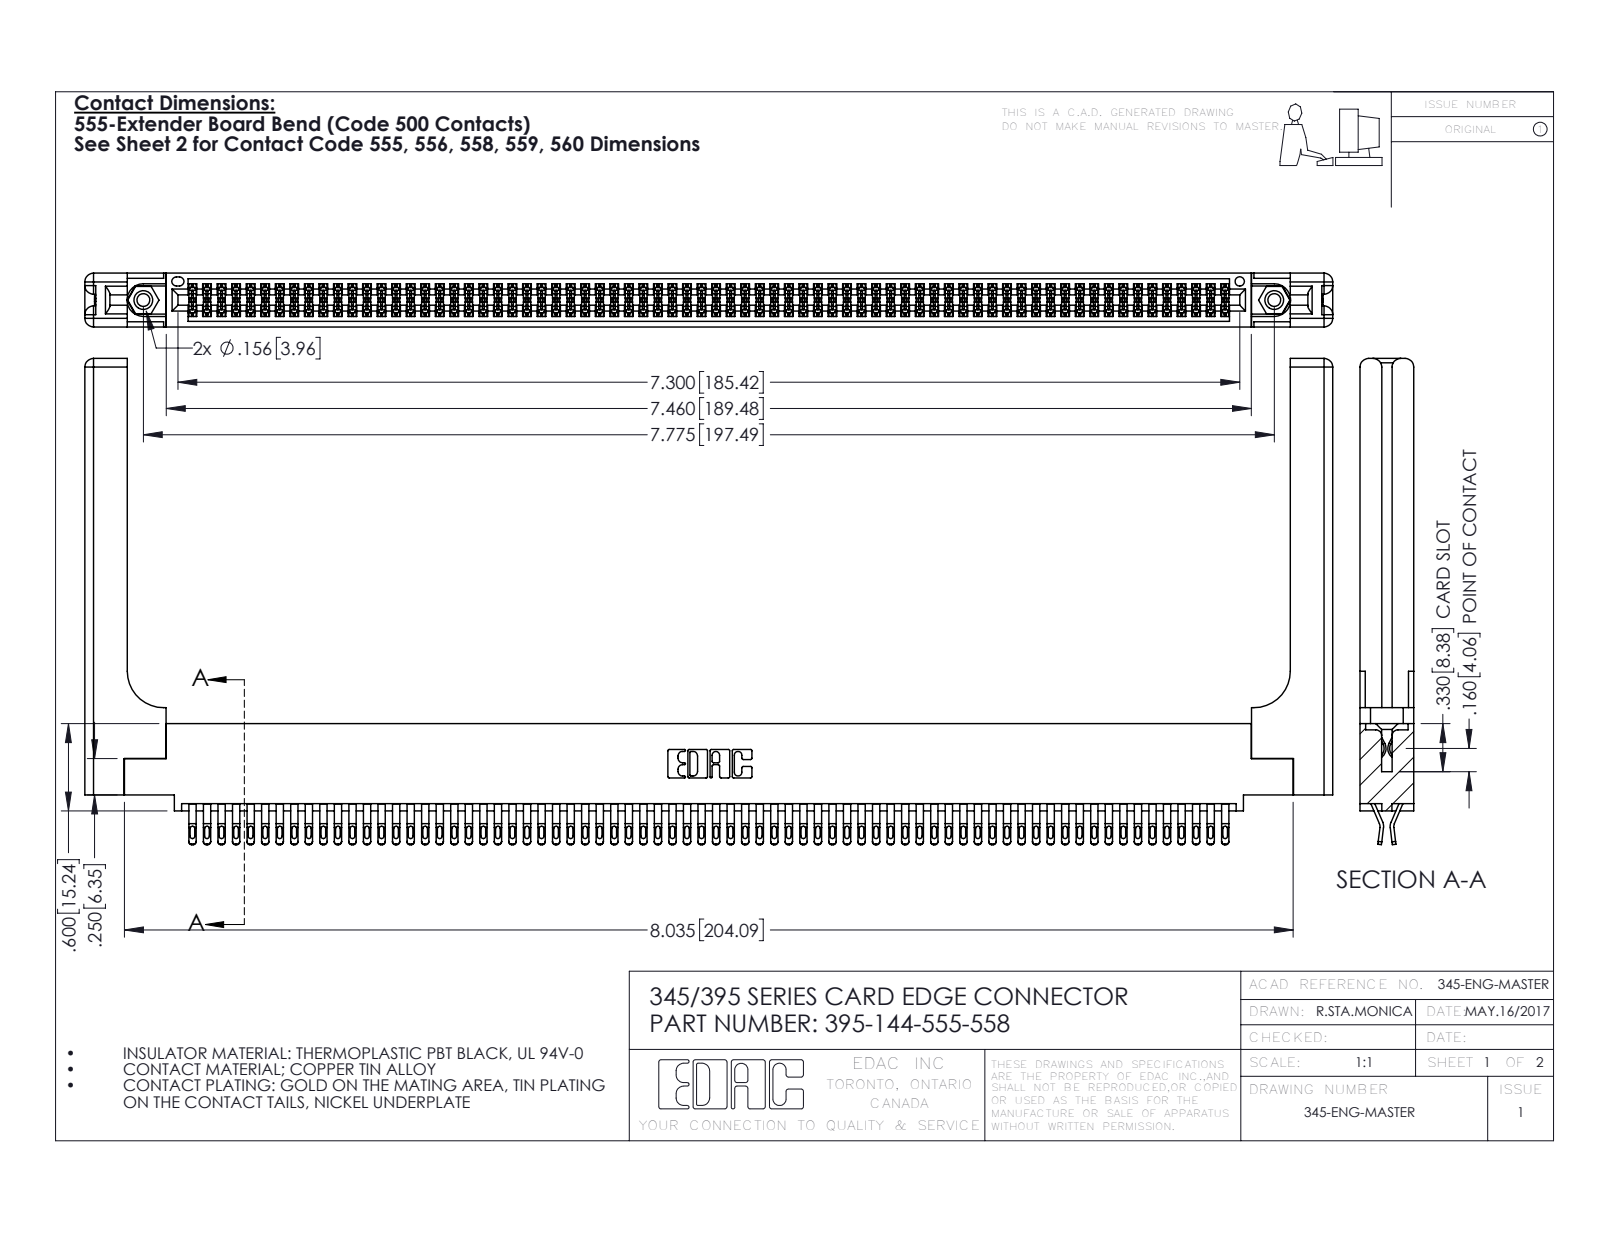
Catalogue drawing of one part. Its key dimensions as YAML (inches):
part_name: "345-220-058_345-220-058; 345-250-001_345-250-001-102; 345 Part_0.110 Offset - 0.156 Dia-TH; 395-144-555-558 (+1 more)"
step_written_by: "SolidWorks 2016 (CONFIG_CONTROL_DESIGN)"
units: inches
bodies: {solids: 149, faces: 8450, planar: 4696, cylindrical: 3694, other: 60}
overall_size: [8.579, 3.342, 0.37]
volume: 1.847
surface_area: 61.06
round_holes:
  - {diameter: 0.089, count: 2}
  - {diameter: 0.125, count: 2}
  - {diameter: 0.156, count: 2}
  - {diameter: 0.064, count: 1}
round_bosses_or_shafts:
  - {diameter: 0.155, count: 2}
partial_cylinders:
  - {radius: 0.016, count: 360}
  - {radius: 0.02, count: 288}
  - {radius: 0.006, count: 216}
  - {radius: 0.01, count: 22}
  - {radius: 0.06, count: 16}
  - {radius: 0.007, count: 6}
  - {radius: 0.031, count: 6}
  - {radius: 0.026, count: 3}
face_to_face_distances: [0.072, 0.298, 0.37, 0.025, 0.098, 0.272, 0.2, 0.225, 0.175, 0.148]
hole_center_spacings: [0.27, 7.539, 7.775]
